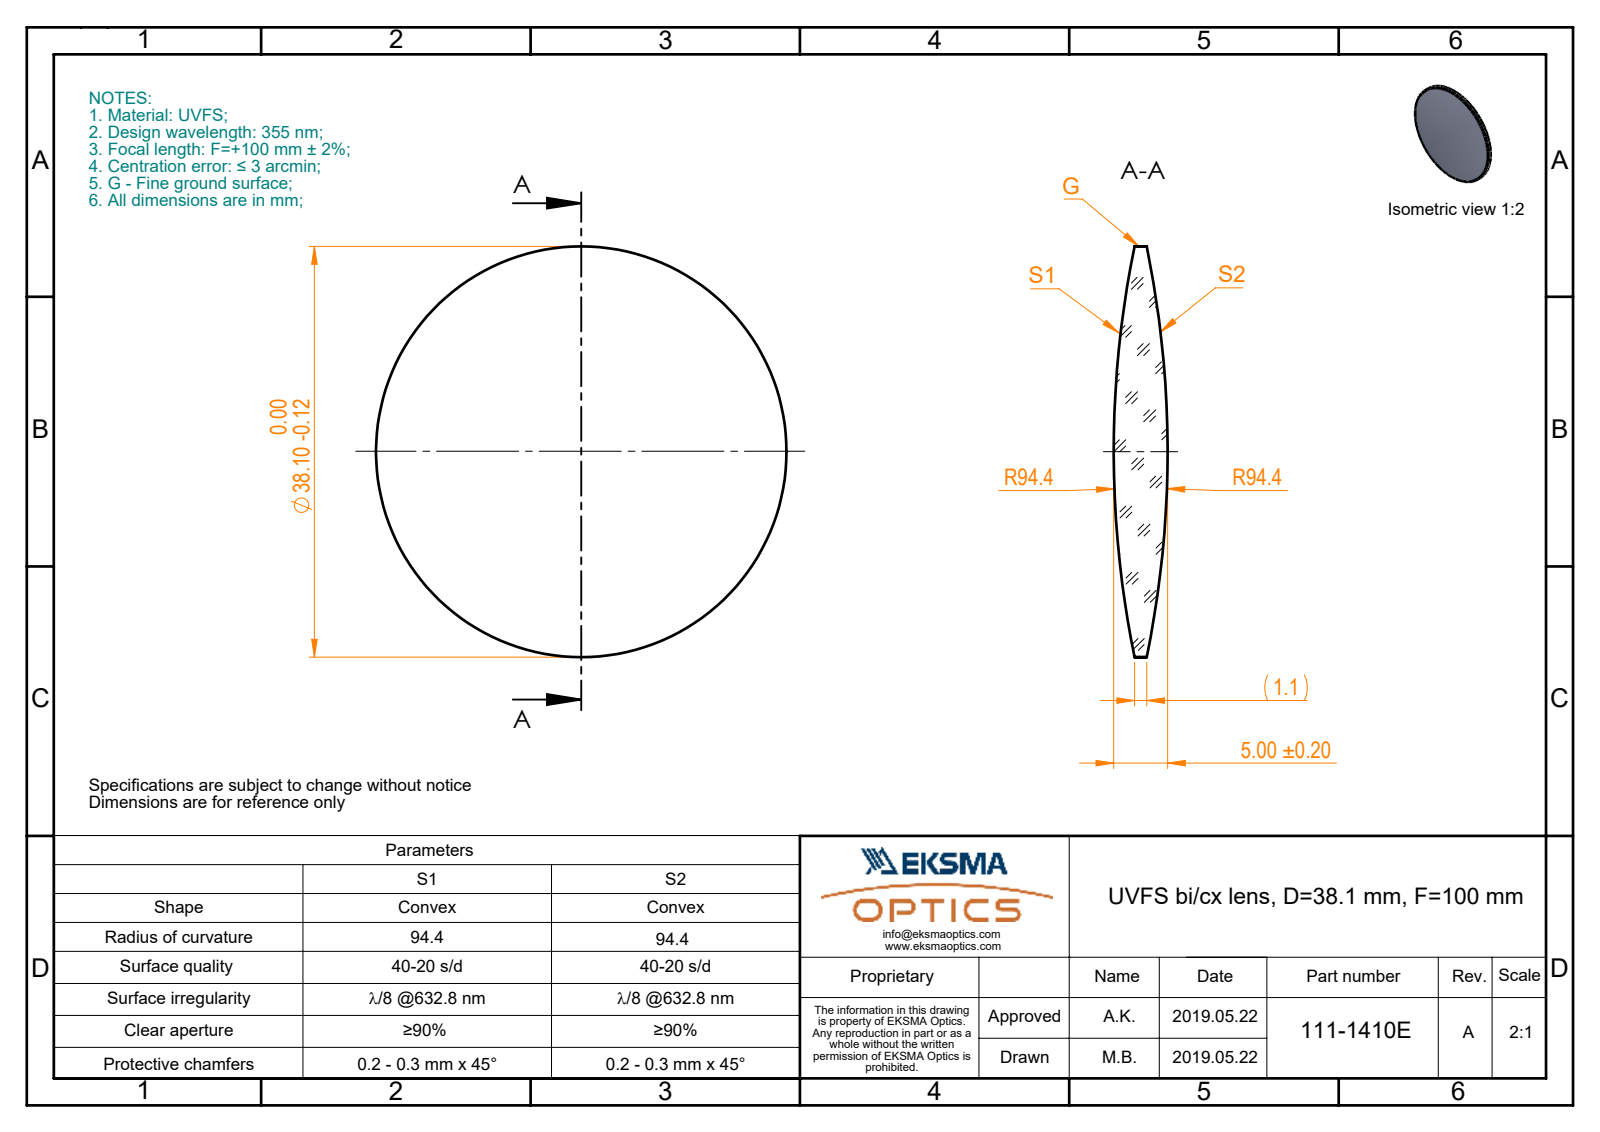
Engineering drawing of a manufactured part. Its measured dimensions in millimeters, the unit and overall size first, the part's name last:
Units: millimetres
Overall size (bounding box): 38.1 × 38.1 × 5
Round bosses / shafts (diameter × count): ⌀38.1 ×1
Volume: 3 494 mm³ · Surface area: 2 437 mm²
Bodies: 1 solid, 6 faces (0 planar, 2 cylindrical, 4 other)
Part name (STEP PRODUCT): 111-1410E UVFS bi-cx 38.1 F100
STEP written by: SolidWorks 2017 (CONFIG_CONTROL_DESIGN)
